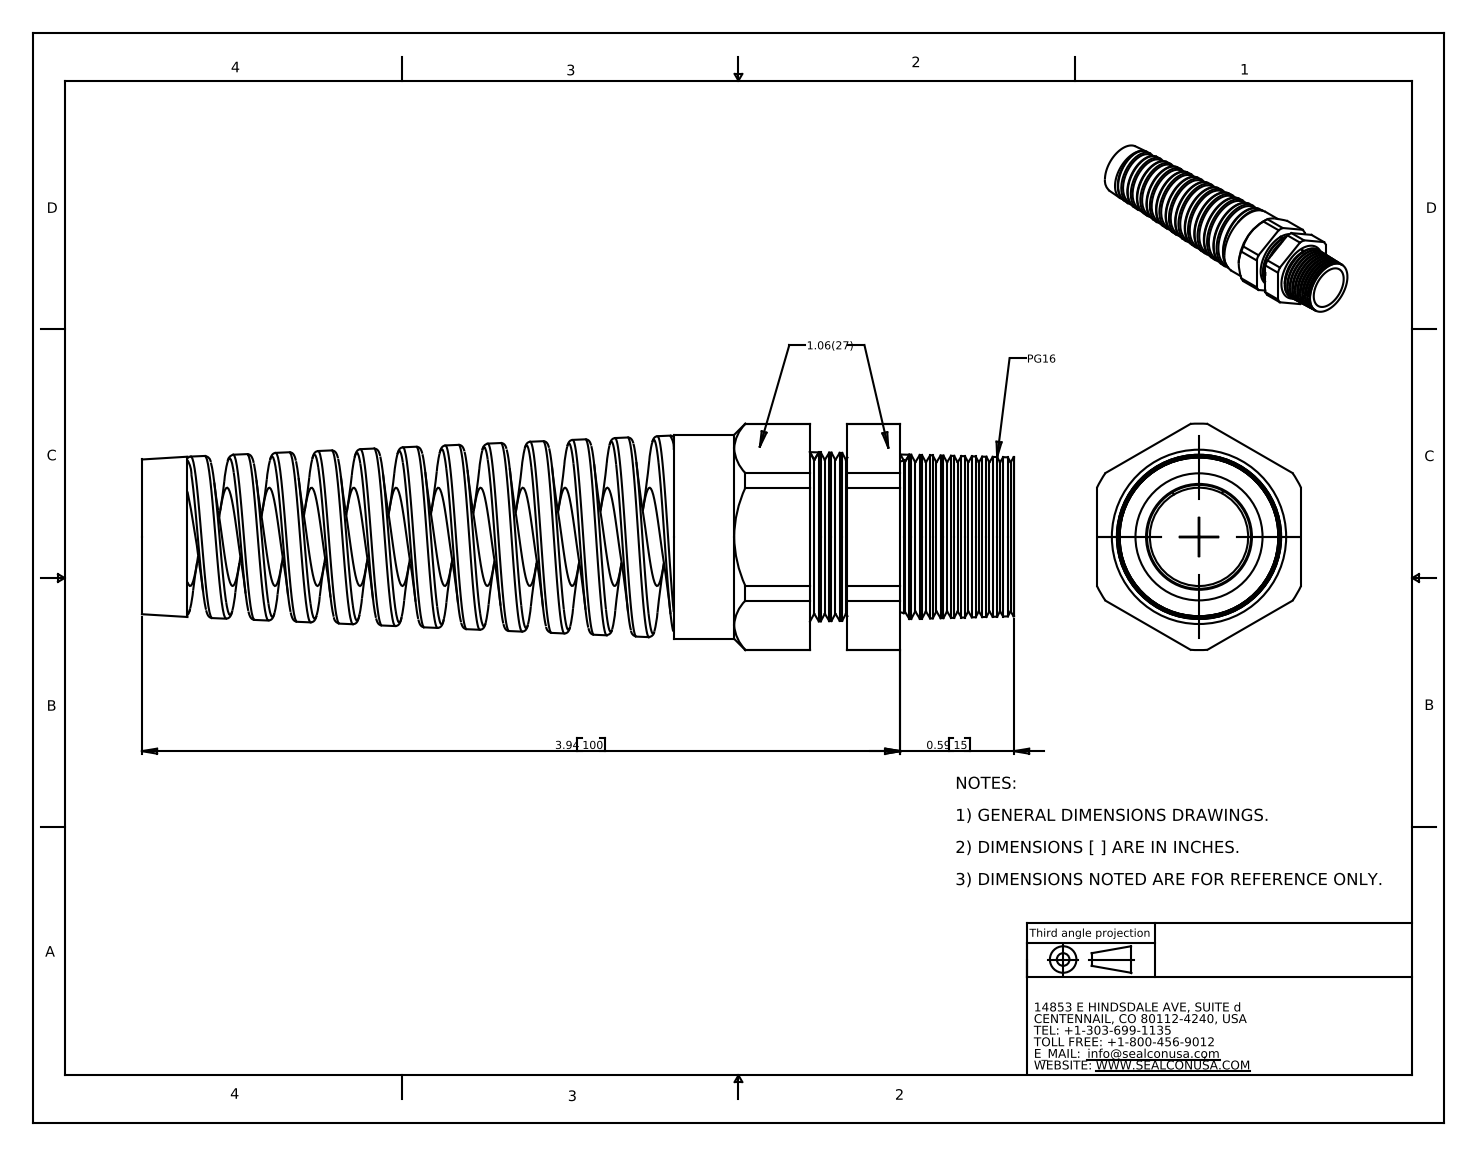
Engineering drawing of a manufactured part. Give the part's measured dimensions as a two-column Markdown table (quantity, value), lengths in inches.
| quantity | value |
| --- | --- |
| part name | CF16CA-GY |
| STEP written by | SolidWorks 2007 (CONFIG_CONTROL_DESIGN) |
| units | inches |
| bodies | 2 solids, 210 faces (24 planar, 49 cylindrical, 137 other) |
| overall size | 4.53 × 1.177 × 1.06 |
| volume | 1.673 in³ |
| surface area | 31.79 in² |
| round holes (diameter × count) | 0.511 × 1, 0.54 × 1, 0.55 × 1 |
| round bosses / shafts (diameter × count) | 1.06 × 1, 0.66 × 1 |
| partial cylindrical surfaces (radius × count) | 0.588 × 1 |
| main face-to-face distances | 1.06, 0.194, 0.47, 0.276, 0.708, 0.902, 1.178, 2.762, 3.47, 3.665 |
